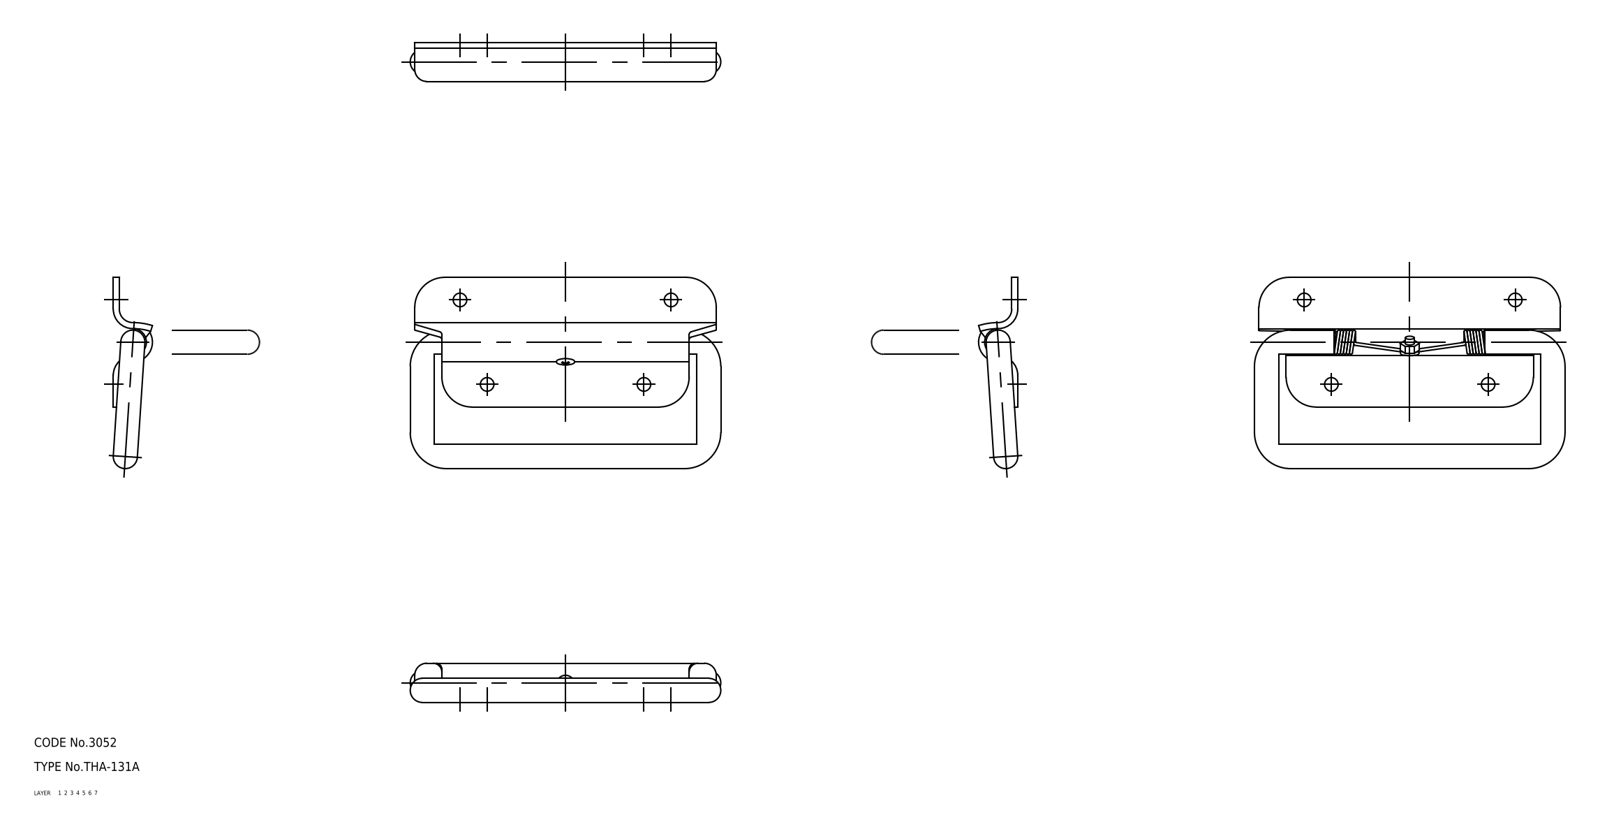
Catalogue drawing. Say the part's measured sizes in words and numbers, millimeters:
The part is named "screw; nut; spring; grip (+2 more)". Its 3-D file was written by "CADfix (AUTOMOTIVE_DESIGN)". It is 5 solids with 192 faces: 0 planar, 0 cylindrical and 192 other. Overall it measures 103 by 63.42 by 13.7 millimeters. Its volume is 19 983 cubic millimeters and its surface area 16 622 square millimeters.
